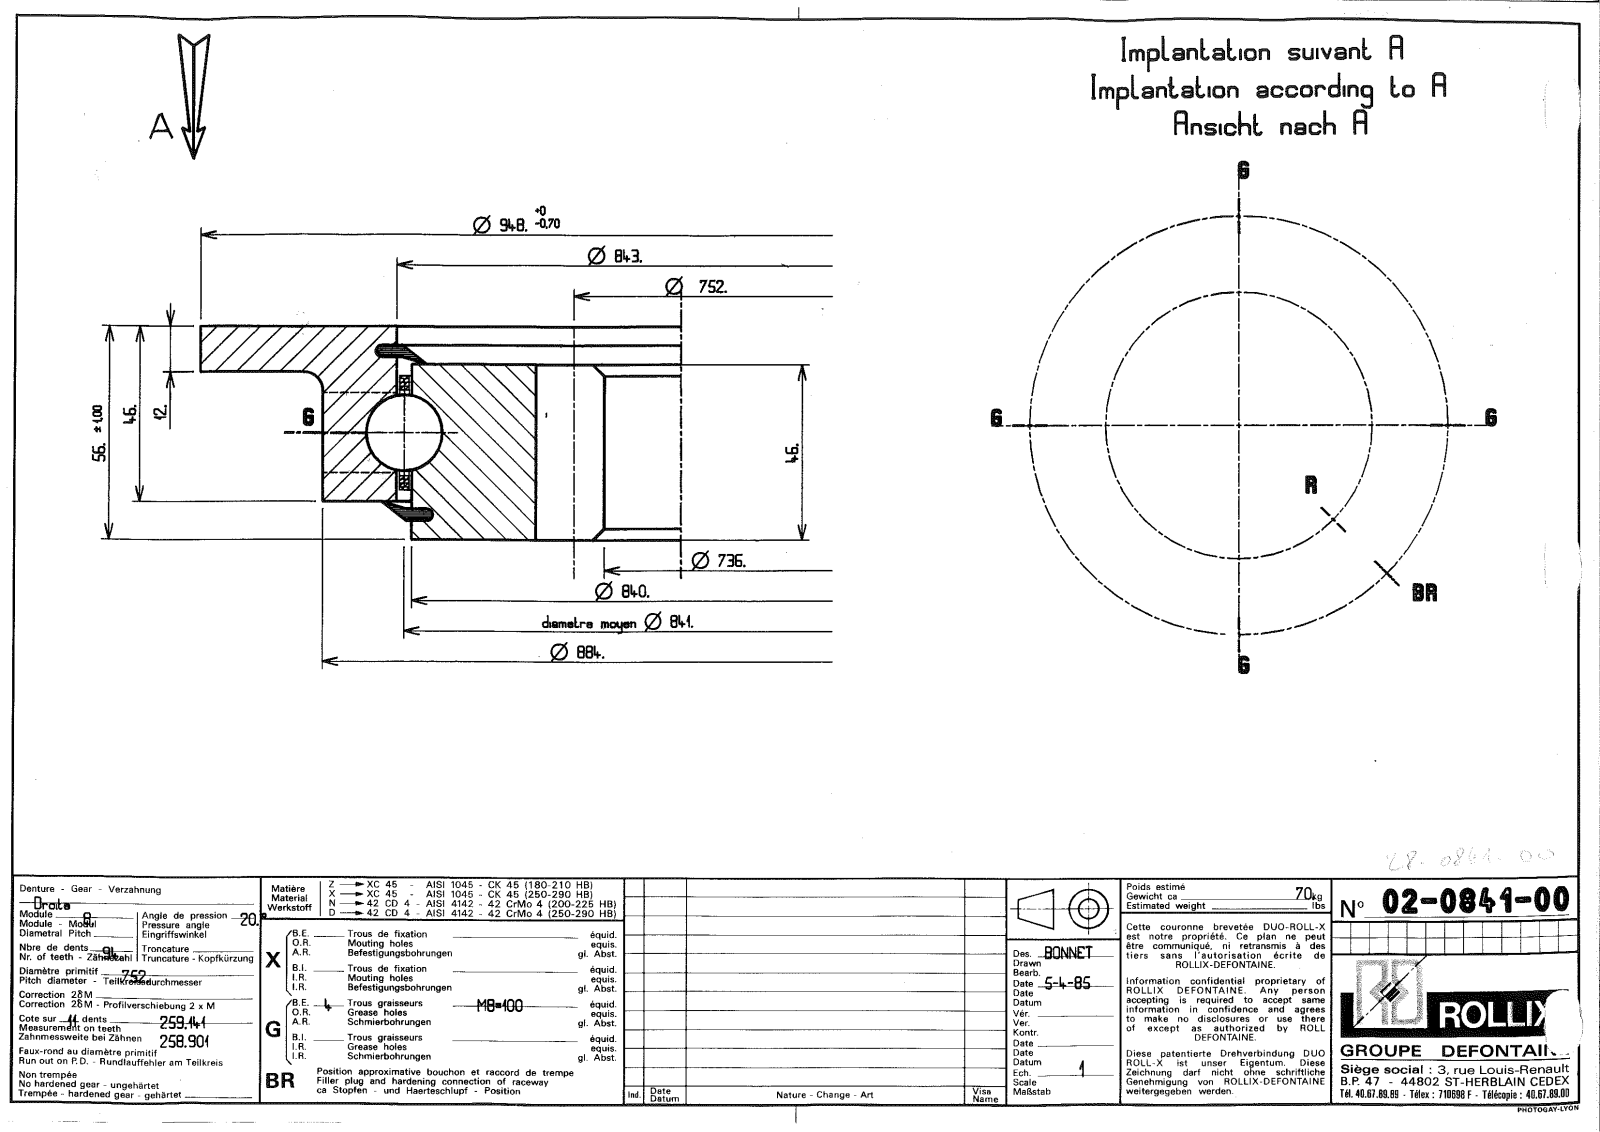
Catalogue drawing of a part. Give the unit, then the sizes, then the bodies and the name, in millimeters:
Units: millimetres
Overall size (bounding box): 948 × 948 × 56
Round holes (diameter × count): ⌀7 ×4, ⌀845.5 ×1
Round bosses / shafts (diameter × count): ⌀8 ×4, ⌀948 ×1, ⌀884 ×1, ⌀836.5 ×1
Partial cylindrical surfaces — rounded edges, fillets, slot ends (radius × count): R368 ×1, R386 ×1
Main face-to-face distances: 10, 46, 56, 44, 2, 12, 34, 36, 4.95, 51.05
Hole centre spacings: 0.52
Volume: 7 835 000 mm³ · Surface area: 1 322 000 mm²
Bodies: 9 solids, 720 faces (241 planar, 221 cylindrical, 258 other)
Part name (STEP PRODUCT): 22-0841-00
STEP written by: SolidWorks 2016 (CONFIG_CONTROL_DESIGN)
